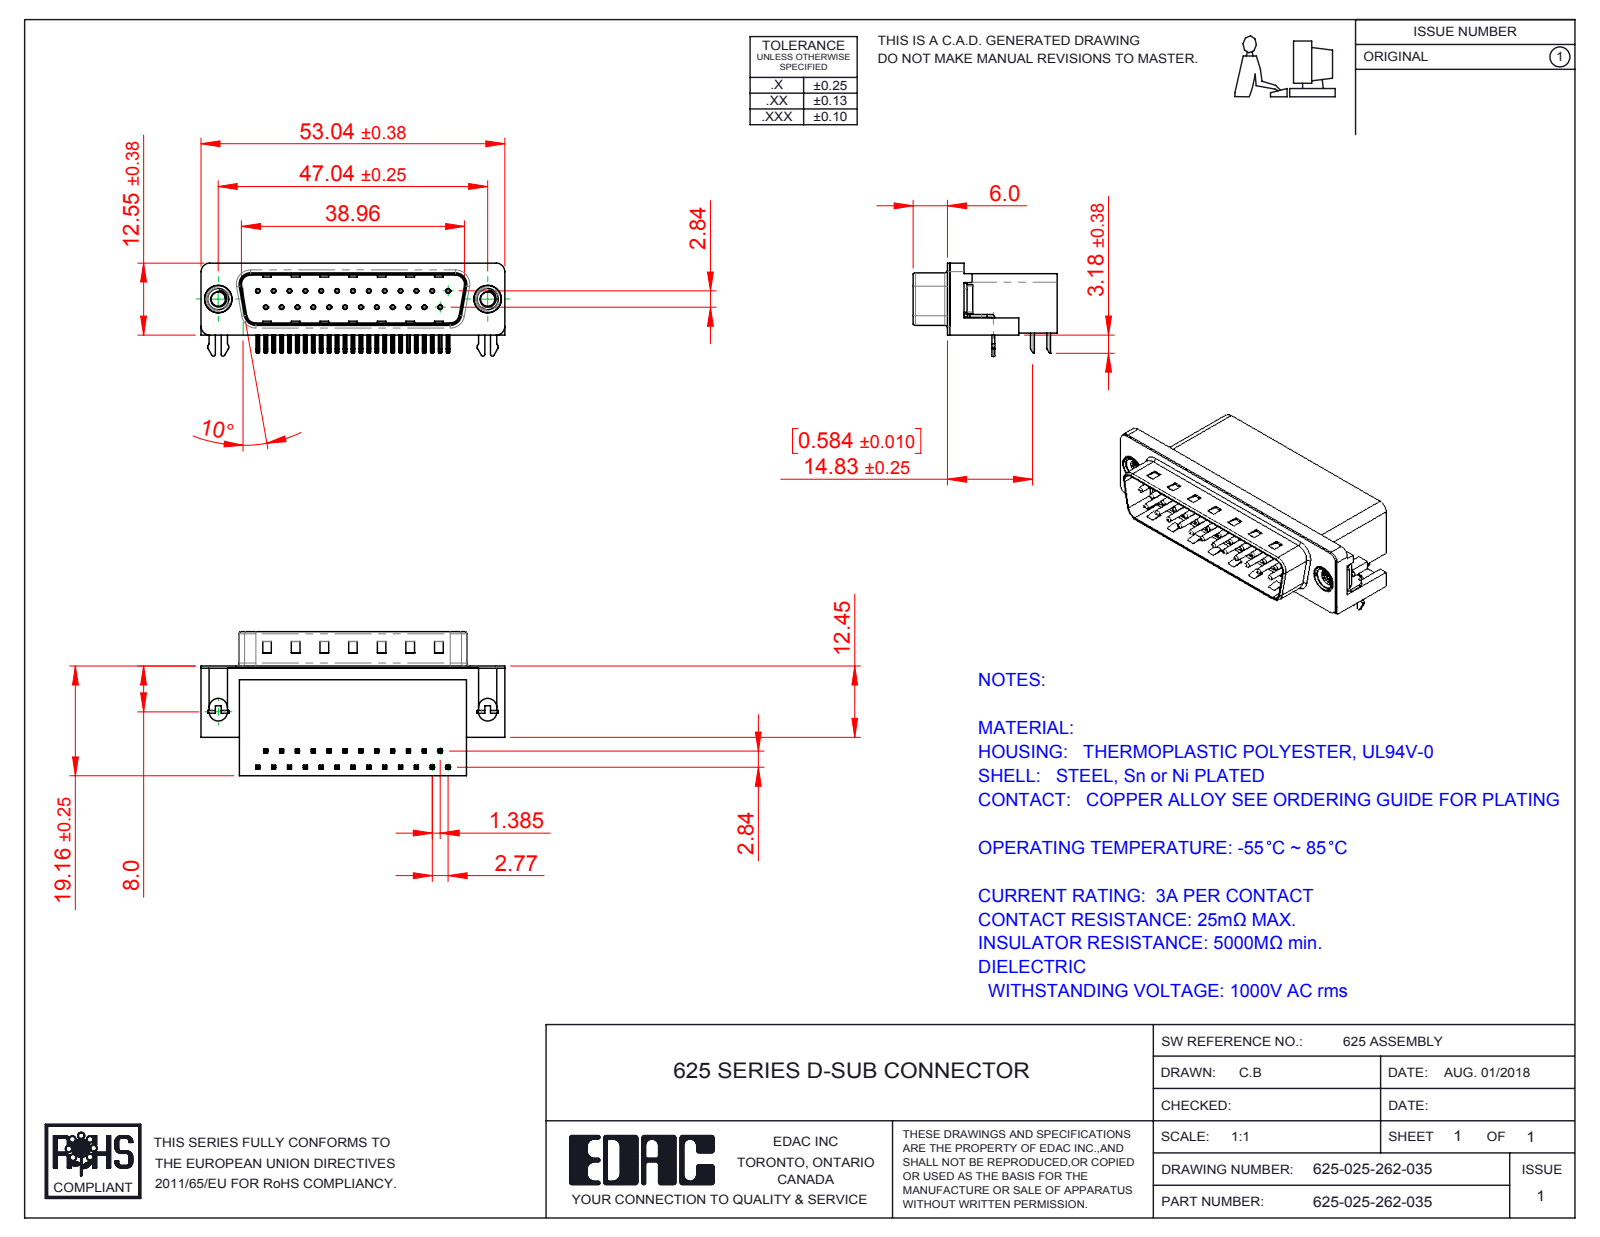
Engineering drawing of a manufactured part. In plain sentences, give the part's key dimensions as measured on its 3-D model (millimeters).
The part is named "625 M3 Threaded Rivet; 625 Shell_25 Socket; 625 Contact Top; 625 Housing_25 Socket (+3 more)". Its 3-D file was written by "SolidWorks 2016 (CONFIG_CONTROL_DESIGN)". It is 31 solids with 2305 faces: 1437 planar, 673 cylindrical and 195 other. Overall it measures 53.04 by 25.16 by 16.25 millimeters. Its volume is 9 158 cubic millimeters and its surface area 8 871 square millimeters. Round holes: 25 of diameter 0.35, 25 of diameter 0.8, 2 of diameter 2.5, 2 of diameter 4, 2 of diameter 4.8, 2 of diameter 5. Round bosses or shafts: 25 of diameter 0.75, 2 of diameter 4.9, 2 of diameter 4.75, 2 of diameter 3.9. Partial cylindrical surfaces (rounded edges, fillets, slot ends): 108 of radius 0.25, 50 of radius 0.12, 16 of radius 1, 14 of radius 0.5, 8 of radius 1.6, 7 of radius 1.5, 4 of radius 0.32, 4 of radius 0.9. The main face-to-face distances are 0.4, 10.35, 18.76, 2.1, 8.76, 10.46, 10.86, 1.7, 19.16, 10.11. The hole center spacings are 3.16, 2.77, 11.08, 5.54, 8.31, 5.03, 13.85, 7.48.
